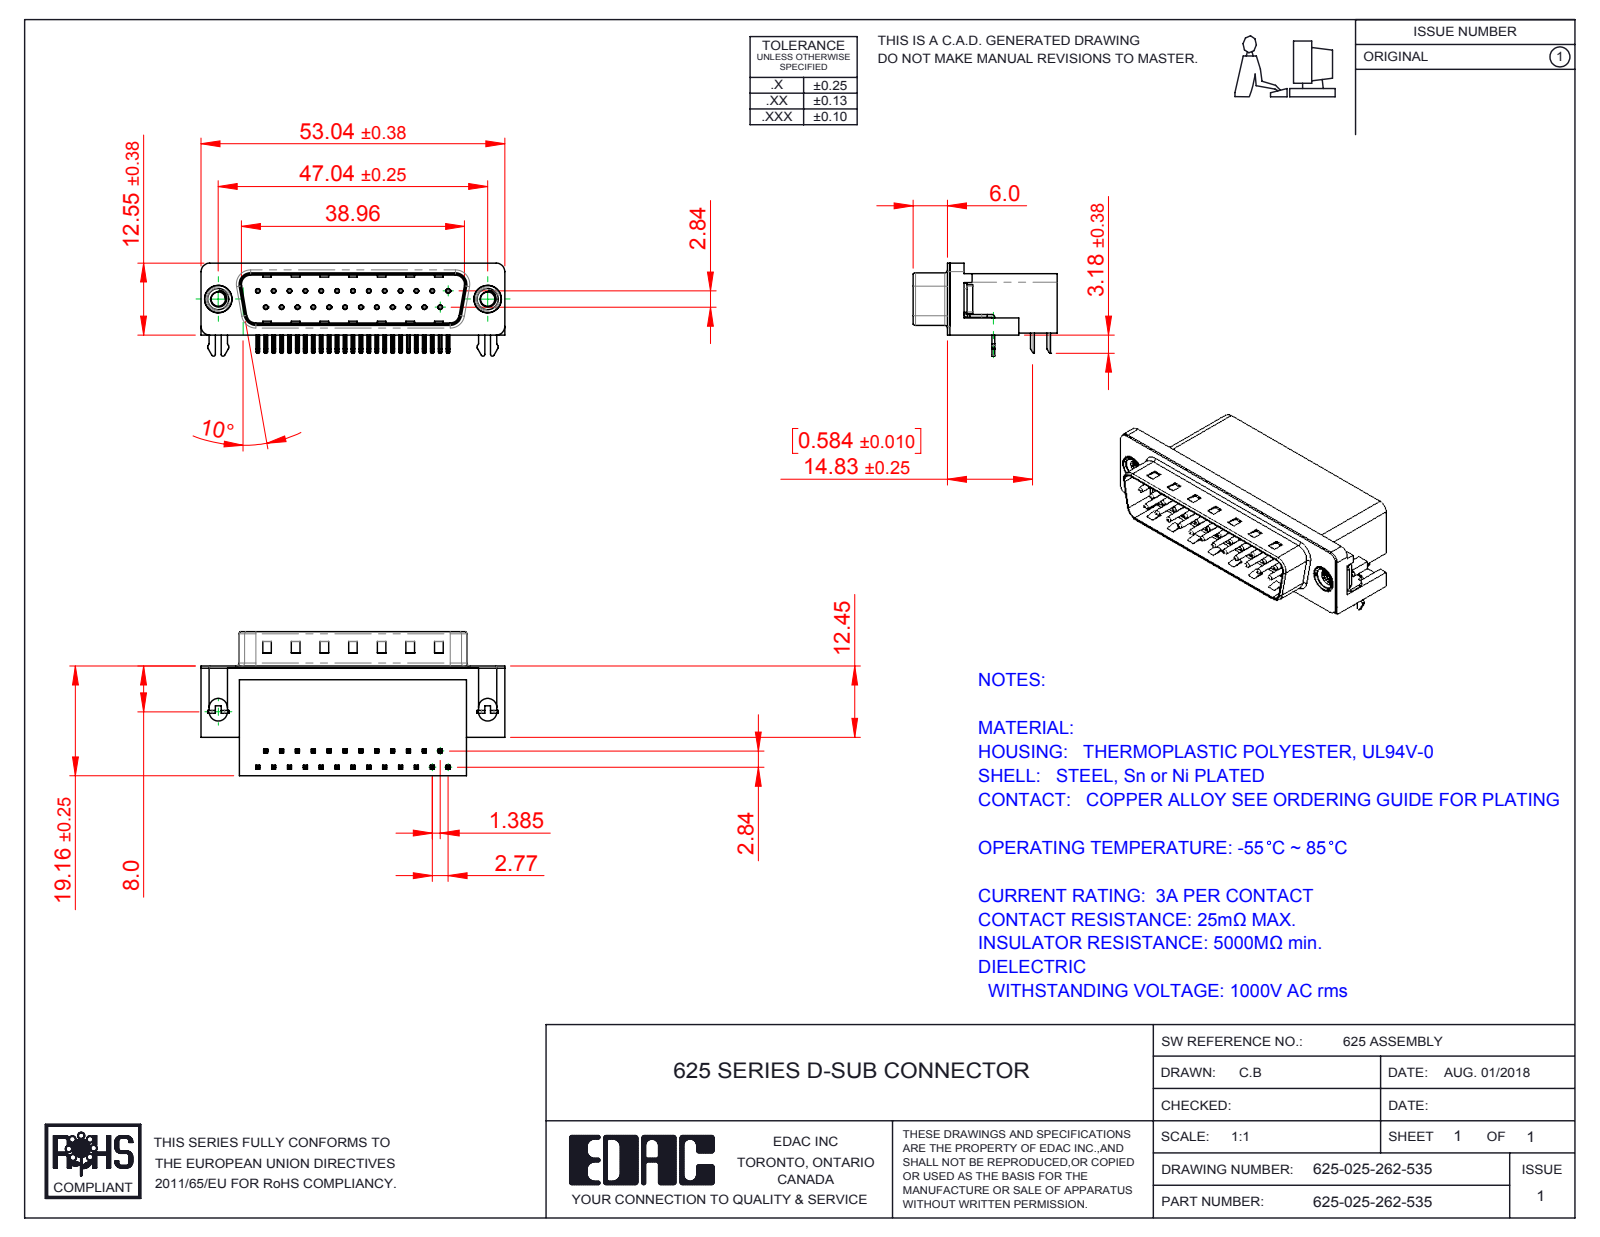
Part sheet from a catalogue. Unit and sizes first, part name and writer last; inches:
Units: inches
Overall size (bounding box): 2.088 × 0.991 × 0.64
Round holes (diameter × count): ⌀0.014 ×25, ⌀0.031 ×25, ⌀0.098 ×2, ⌀0.157 ×2, ⌀0.189 ×2, ⌀0.197 ×2
Round bosses / shafts (diameter × count): ⌀0.03 ×25, ⌀0.193 ×2, ⌀0.187 ×2, ⌀0.154 ×2
Partial cylindrical surfaces — rounded edges, fillets, slot ends (radius × count): R0.01 ×108, R0.005 ×50, R0.039 ×16, R0.02 ×14, R0.063 ×8, R0.059 ×7, R0.013 ×4, R0.035 ×4
Main face-to-face distances: 0.016, 0.407, 0.739, 0.083, 0.345, 0.412, 0.428, 0.067, 0.754, 0.398
Hole centre spacings: 0.124, 0.109, 0.436, 0.218, 0.327, 0.198, 0.545, 0.294
Volume: 0.559 in³ · Surface area: 13.75 in²
Bodies: 31 solids, 2305 faces (1437 planar, 673 cylindrical, 195 other)
Part name (STEP PRODUCT): 625 Shell_25 Socket; 625 Housing_25 Socket; 625 2 Prong Board Lock; 625-025-262-535 (+3 more)
STEP written by: SolidWorks 2016 (CONFIG_CONTROL_DESIGN)
